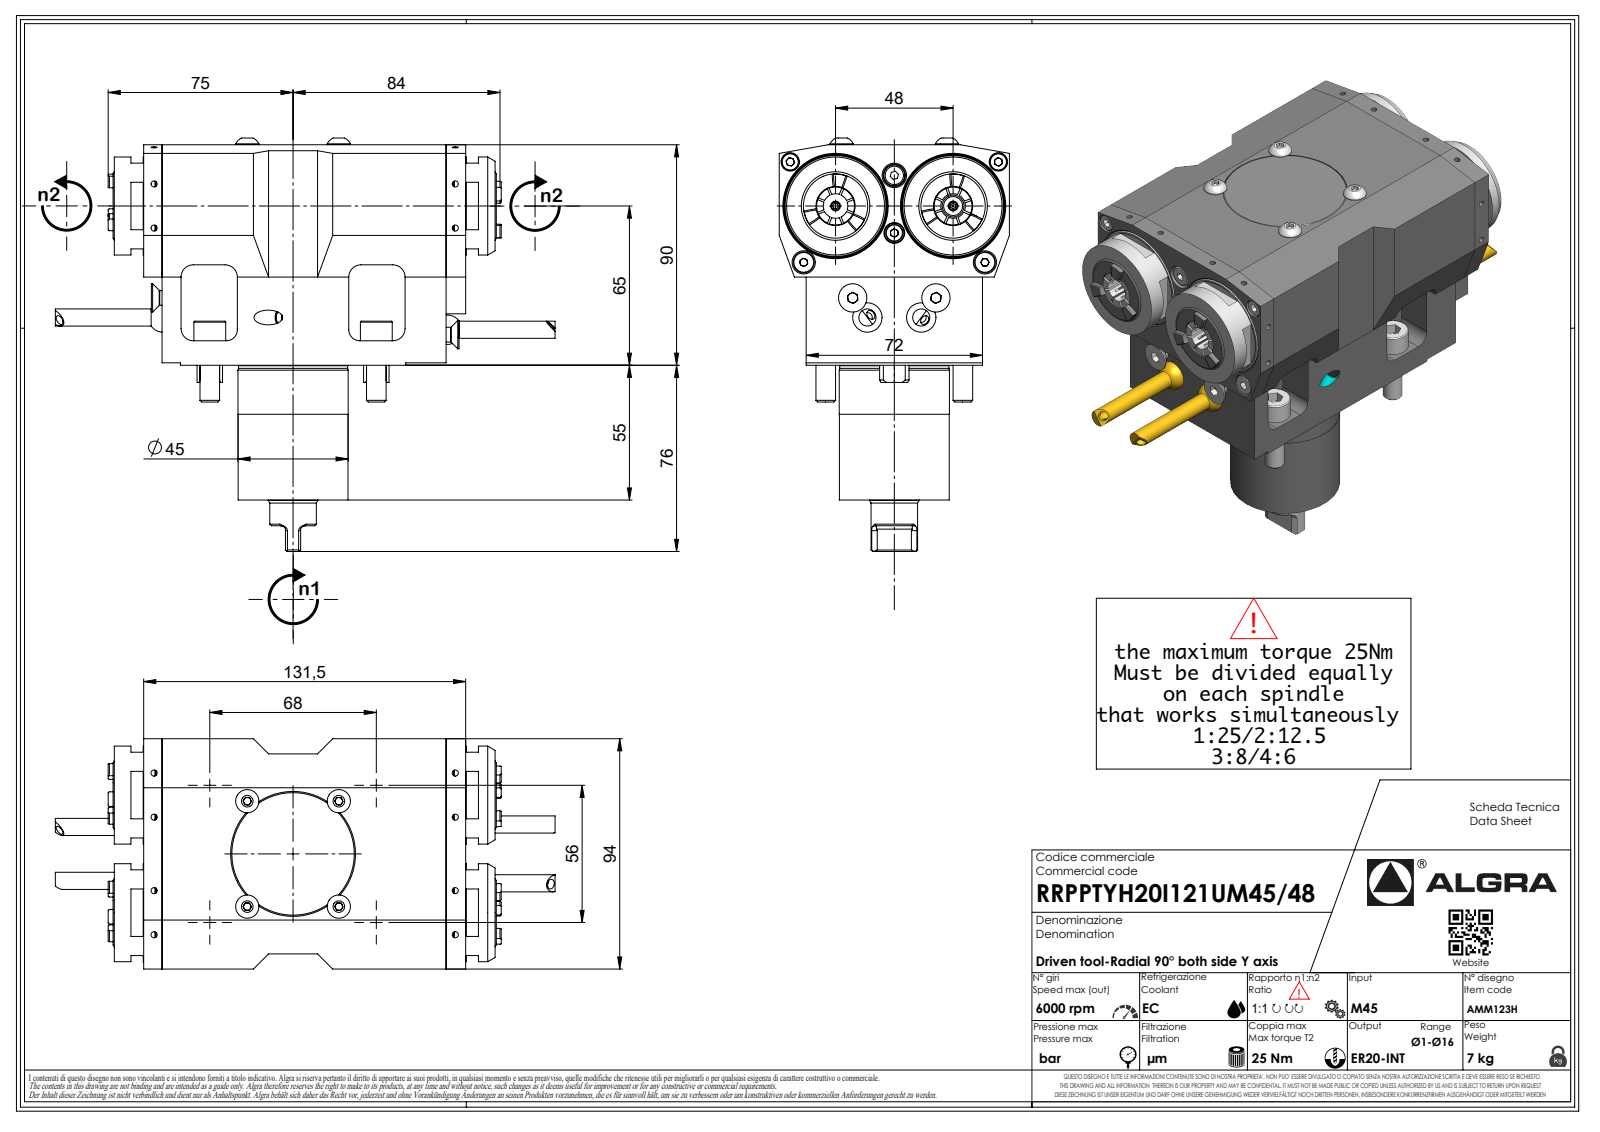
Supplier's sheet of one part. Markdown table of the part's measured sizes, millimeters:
| quantity | value |
| --- | --- |
| part name | RRPPTYH20I121UM4548 |
| STEP written by | SolidWorks 2023 (AUTOMOTIVE_DESIGN) |
| units | millimeters |
| bodies | 5 solids, 842 faces (440 planar, 149 cylindrical, 253 other) |
| overall size | 204.08 × 166 × 94 |
| volume | 1 123 000 mm³ |
| surface area | 92 294 mm² |
| round holes (diameter × count) | 4 × 4, 5 × 2, 16 × 2, 2.1 × 1 |
| round bosses / shafts (diameter × count) | 7 × 4, 8 × 3, 40 × 2, 28 × 2, 45 × 1, 44.85 × 1, 20.3 × 1, 19 × 1 |
| partial cylindrical surfaces (radius × count) | 32.53 × 20, 2 × 10, 0.33 × 7, 0.52 × 7, 3.7 × 7, 5 × 2, 6 × 2, 13 × 2 |
| main face-to-face distances | 83, 11, 90, 94, 72, 12, 143.5, 7.5, 20, 35 |
| hole center spacings | 48, 68 |
